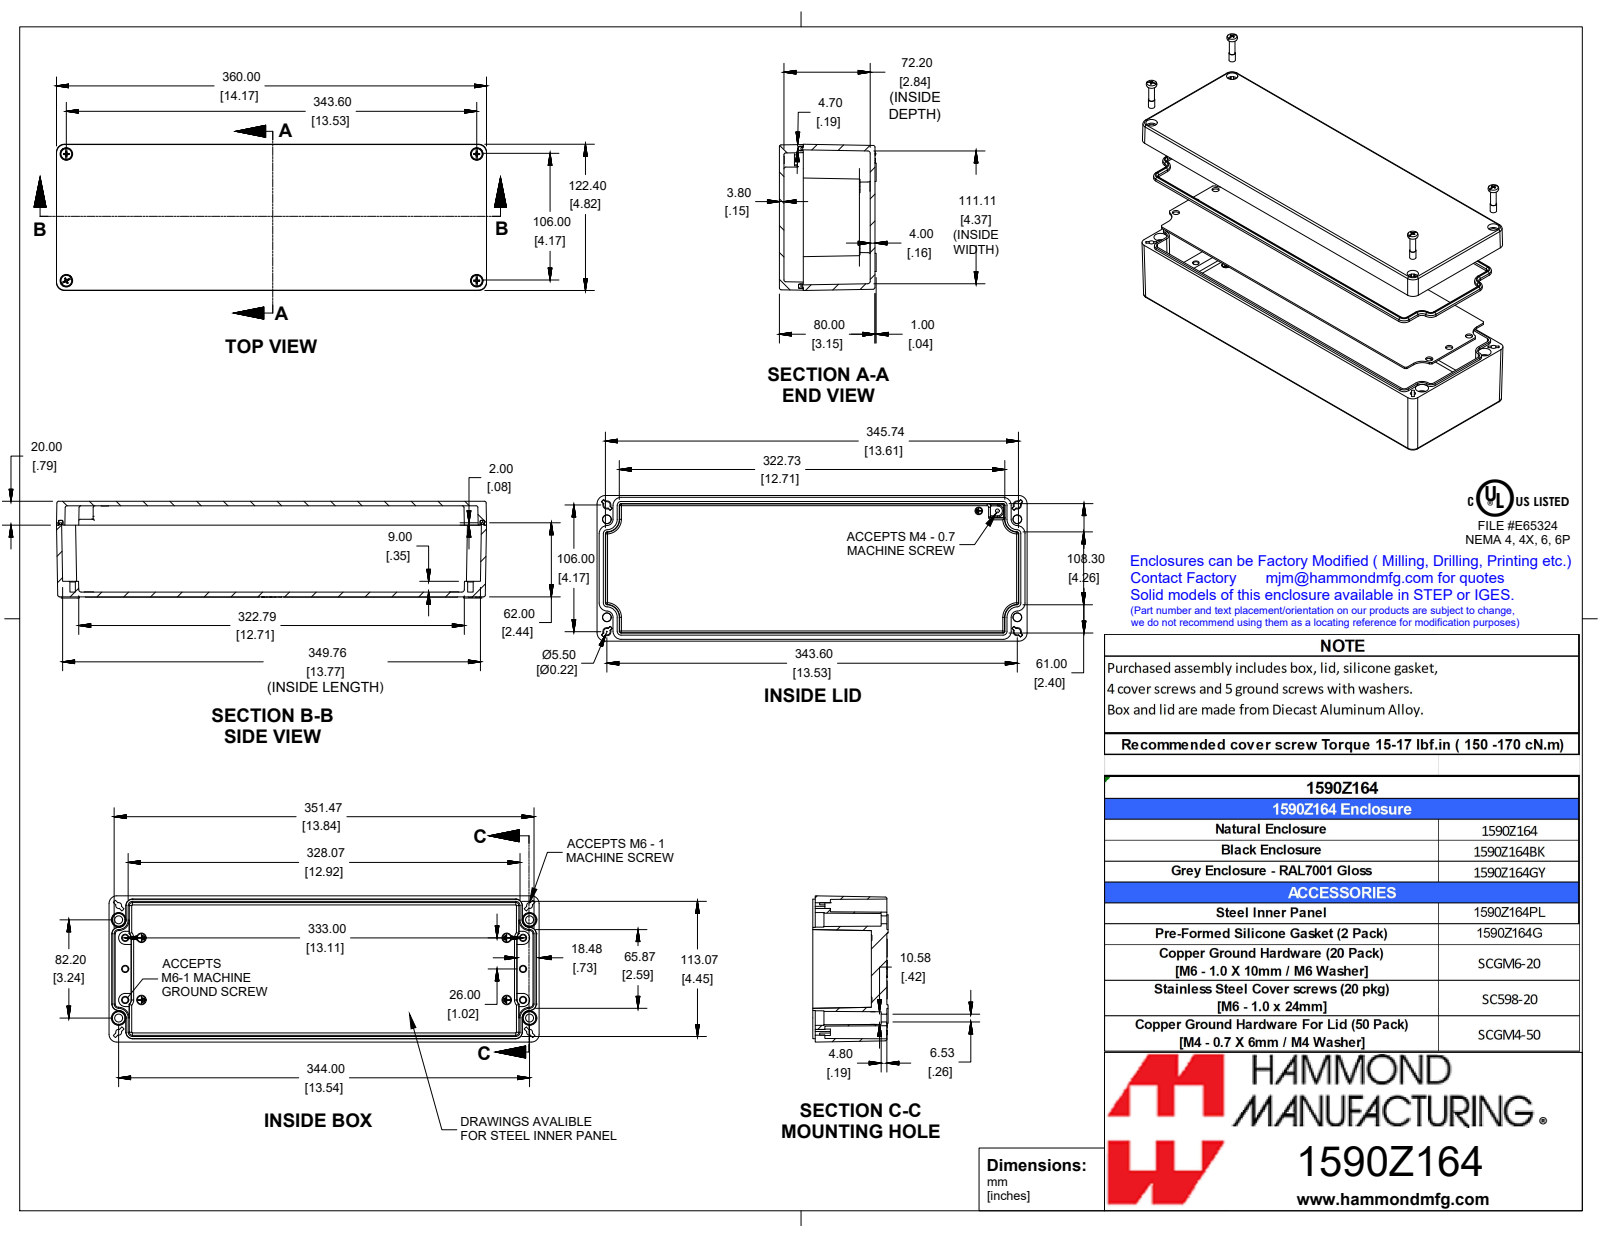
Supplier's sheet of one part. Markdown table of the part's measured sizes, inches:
| quantity | value |
| --- | --- |
| part name | 1590Z164GY |
| STEP written by | SolidWorks 2019 (CONFIG_CONTROL_DESIGN) |
| units | inches |
| bodies | 8 solids, 1057 faces (544 planar, 176 cylindrical, 337 other) |
| overall size | 14.173 × 4.819 × 3.201 |
| volume | 45.02 in³ |
| surface area | 667.9 in² |
| round holes (diameter × count) | 0.194 × 6, 0.257 × 6, 0.26 × 4, 0.276 × 4, 0.413 × 4, 0.48 × 4, 0.128 × 1 |
| round bosses / shafts (diameter × count) | 0.236 × 4, 0.231 × 4, 0.208 × 4 |
| partial cylindrical surfaces (radius × count) | 0.059 × 44, 0.128 × 8, 0.258 × 8, 0.039 × 7, 0.097 × 4, 0.108 × 4, 0.134 × 4, 0.203 × 4 |
| main face-to-face distances | 3.161, 0.453, 0.185, 0.098, 3.063, 0.354, 2.709, 0.071, 3.012, 2.913 |
| hole center spacings | 13.152, 0.037, 0.469, 0.627, 0.64, 1.004, 1.004, 1.027 |
